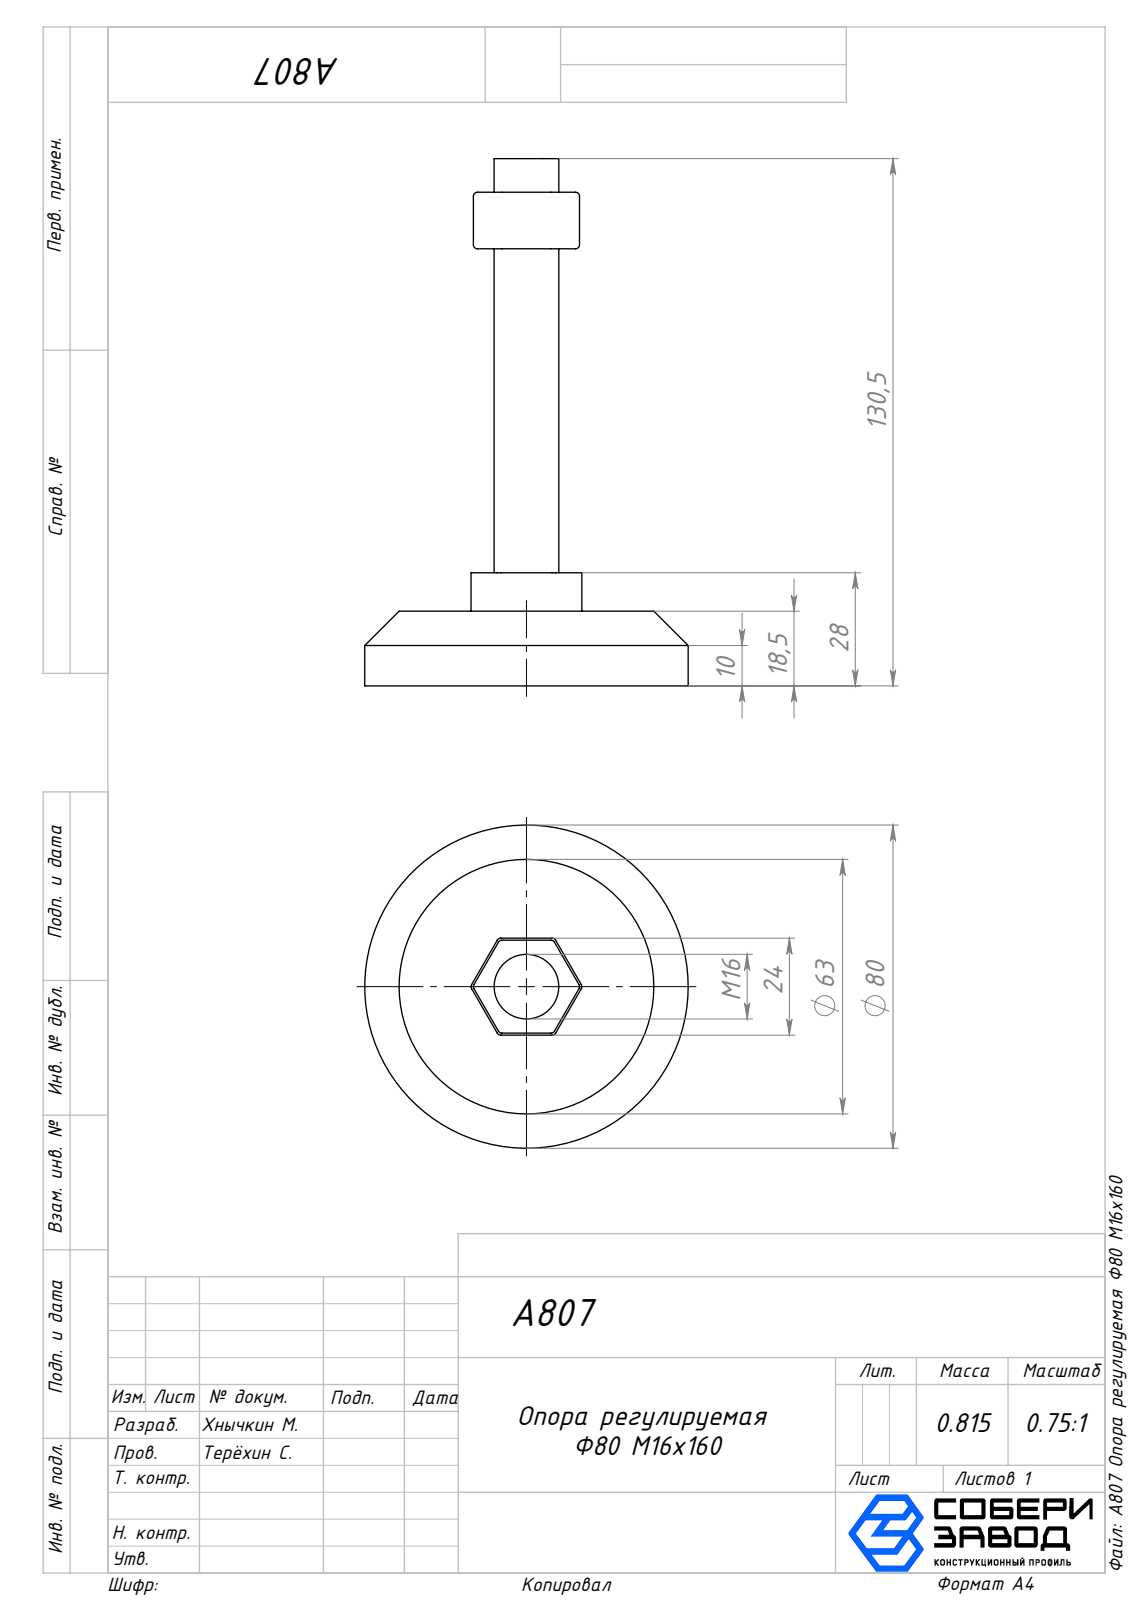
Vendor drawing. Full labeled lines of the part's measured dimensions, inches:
Part name (STEP PRODUCT): A807 Опора регулируемая Ф80 М16х160; Вал M16_00; hex bolt gradeab_din_DIN EN 24014 - M5 x 25 x 16-N; Опора_00 (+1 more)
STEP written by: SolidWorks 2025 (AUTOMOTIVE_DESIGN)
Units: inches
Bodies: 4 solids, 110 faces (36 planar, 44 cylindrical, 30 other)
Overall size (bounding box): 5.138 × 3.15 × 3.15
Volume: 6.74 in³ · Surface area: 38.4 in²
Round holes (diameter × count): ⌀0.205 ×1, ⌀0.551 ×1, ⌀1.063 ×1
Round bosses / shafts (diameter × count): ⌀3.15 ×1, ⌀0.63 ×1, ⌀0.315 ×1, ⌀0.197 ×1
Partial cylindrical surfaces — rounded edges, fillets, slot ends (radius × count): R0.039 ×24
Main face-to-face distances: 0.728, 0.02, 0.925, 0.906, 0.276, 0.453, 0.945, 1.102, 0.827, 0.374
